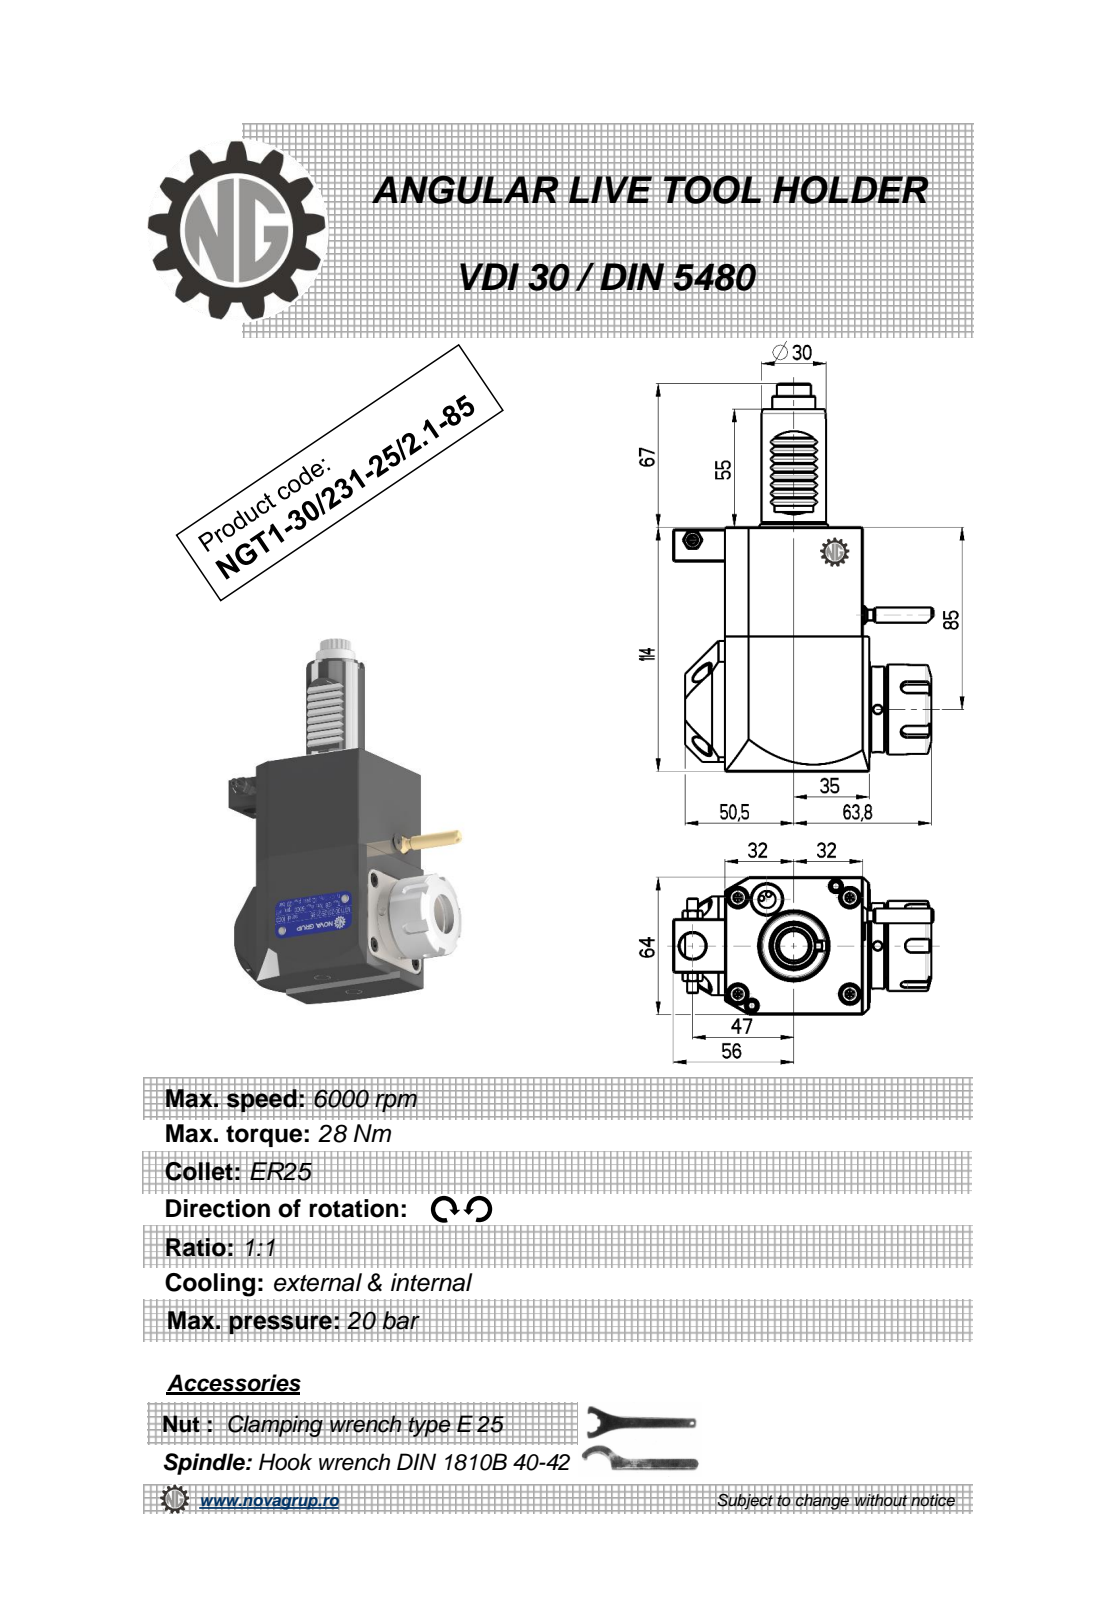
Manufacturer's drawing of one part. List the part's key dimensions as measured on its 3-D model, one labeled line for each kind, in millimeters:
Part name (STEP PRODUCT): NGT1_30_231_25_2_1_85
STEP written by: PRO/ENGINEER BY PARAMETRIC TECHNOLOGY CORPORATION, 2010280 (CONFIG_CONTROL_DESIGN)
Units: millimetres
Bodies: 1 solid, 498 faces (184 planar, 157 cylindrical, 157 other)
Overall size (bounding box): 181 × 120.88 × 65.6
Volume: 583 096 mm³ · Surface area: 55 084 mm²
Round holes (diameter × count): ⌀4 ×2, ⌀2.5 ×1, ⌀3 ×1, ⌀4.2 ×1, ⌀9.5 ×1, ⌀12 ×1, ⌀20.3 ×1
Round bosses / shafts (diameter × count): ⌀8.96 ×2, ⌀5 ×2, ⌀42 ×1, ⌀40 ×1, ⌀33 ×1, ⌀30 ×1, ⌀20 ×1, ⌀7 ×1
Partial cylindrical surfaces — rounded edges, fillets, slot ends (radius × count): R1.98 ×36, R0.26 ×12, R0.3 ×8, R3 ×5, R160 ×2, R7.08 ×1, R7.92 ×1, R13 ×1
Main face-to-face distances: 64, 114, 67.2, 3.2, 67, 3, 18.5, 0.5, 82.5, 85.5
Hole centre spacings: 35.39, 46.17, 76.5, 85.95, 116.74
